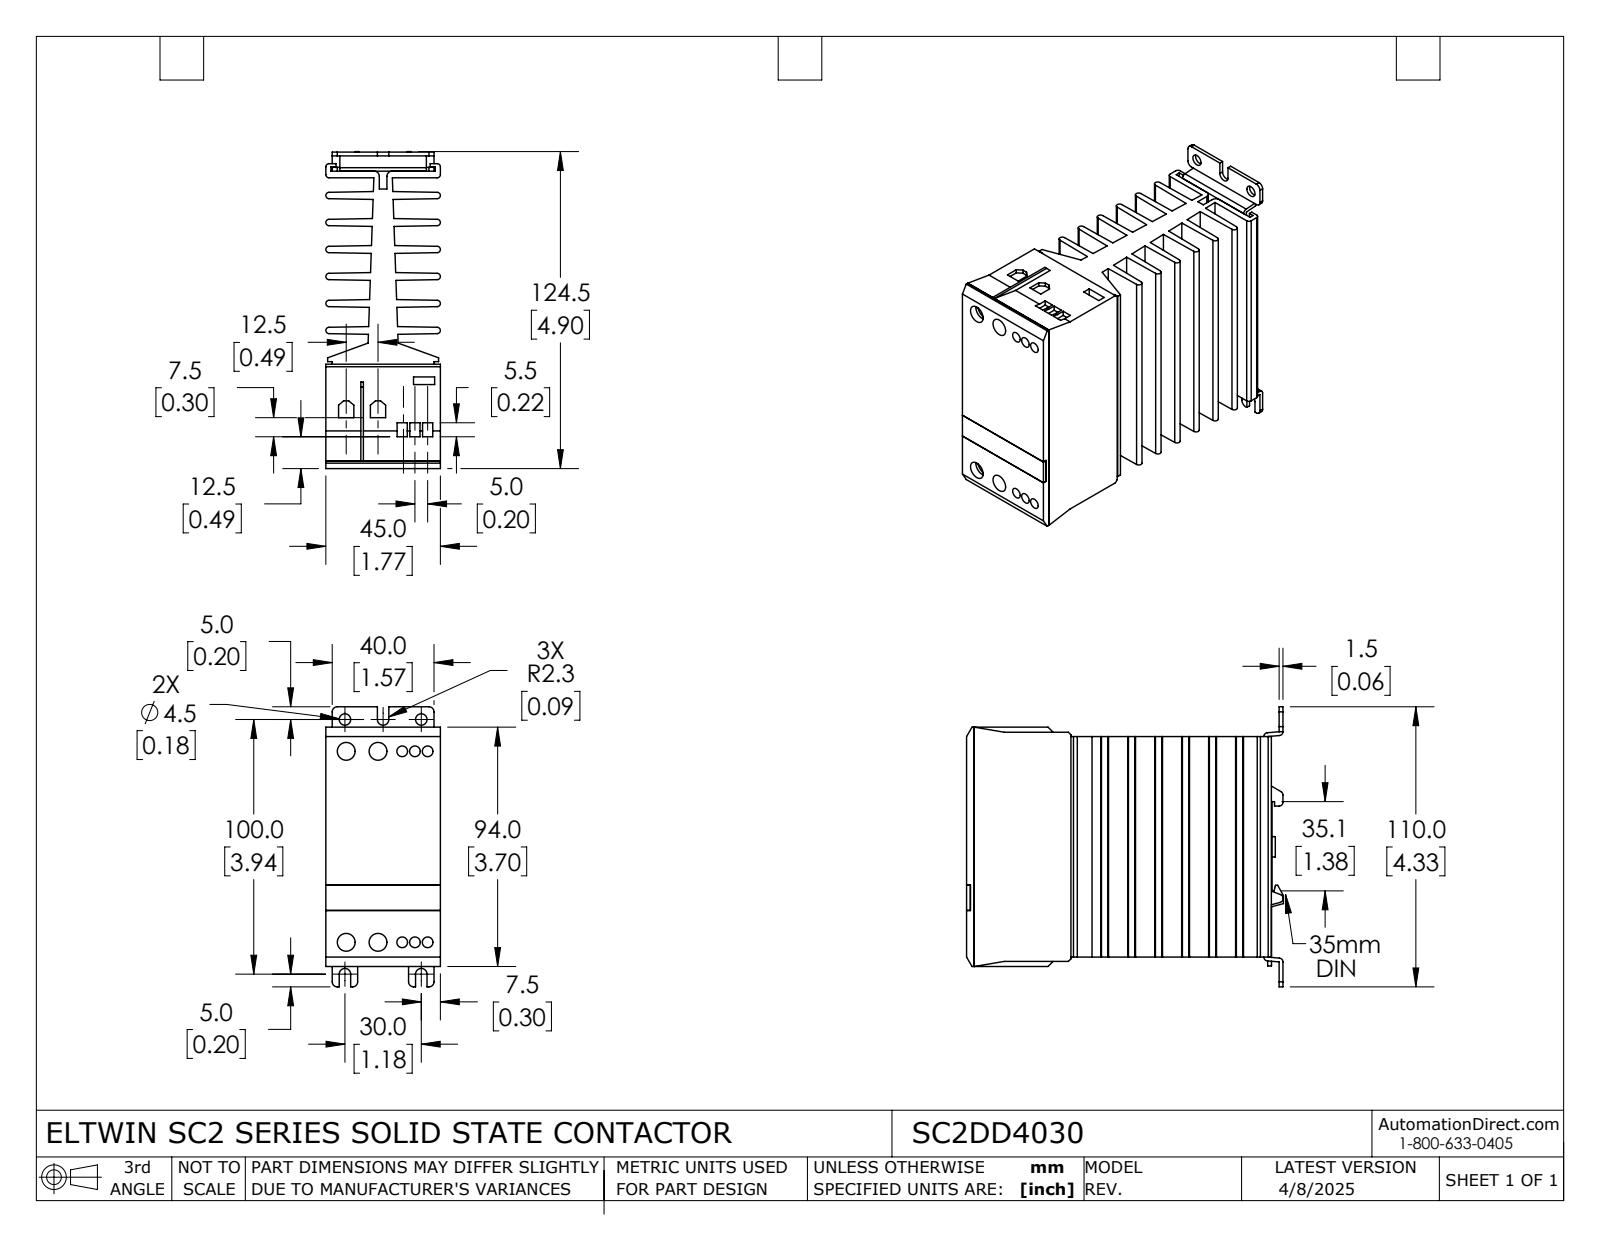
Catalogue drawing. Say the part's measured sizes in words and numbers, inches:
The part is named "SC2DD4030". Its 3-D file was written by "SolidWorks 2021 (AUTOMOTIVE_DESIGN)". It is 7 solids with 391 faces: 284 planar, 107 cylindrical and 0 other. Overall it measures 4.902 by 4.331 by 1.772 inches. Its volume is 18.87 cubic inches and its surface area 165.4 square inches. Round holes: 6 of diameter 0.165, 6 of diameter 0.173, 4 of diameter 0.276, 2 of diameter 0.177, 2 of diameter 0.315. Round bosses or shafts: 3 of diameter 0.315. Partial cylindrical surfaces (rounded edges, fillets, slot ends): 18 of radius 0.079, 16 of radius 0.049, 10 of radius 0.059, 4 of radius 0.051, 3 of radius 0.089. The main face-to-face distances are 0.417, 0.835, 0.127, 1.252, 0.29, 0.544, 0.707, 0.962, 1.669, 1.125. The hole center spacings are 2.953, 0.197, 2.959, 0.374, 0.394, 0.492, 0.502, 0.571.
